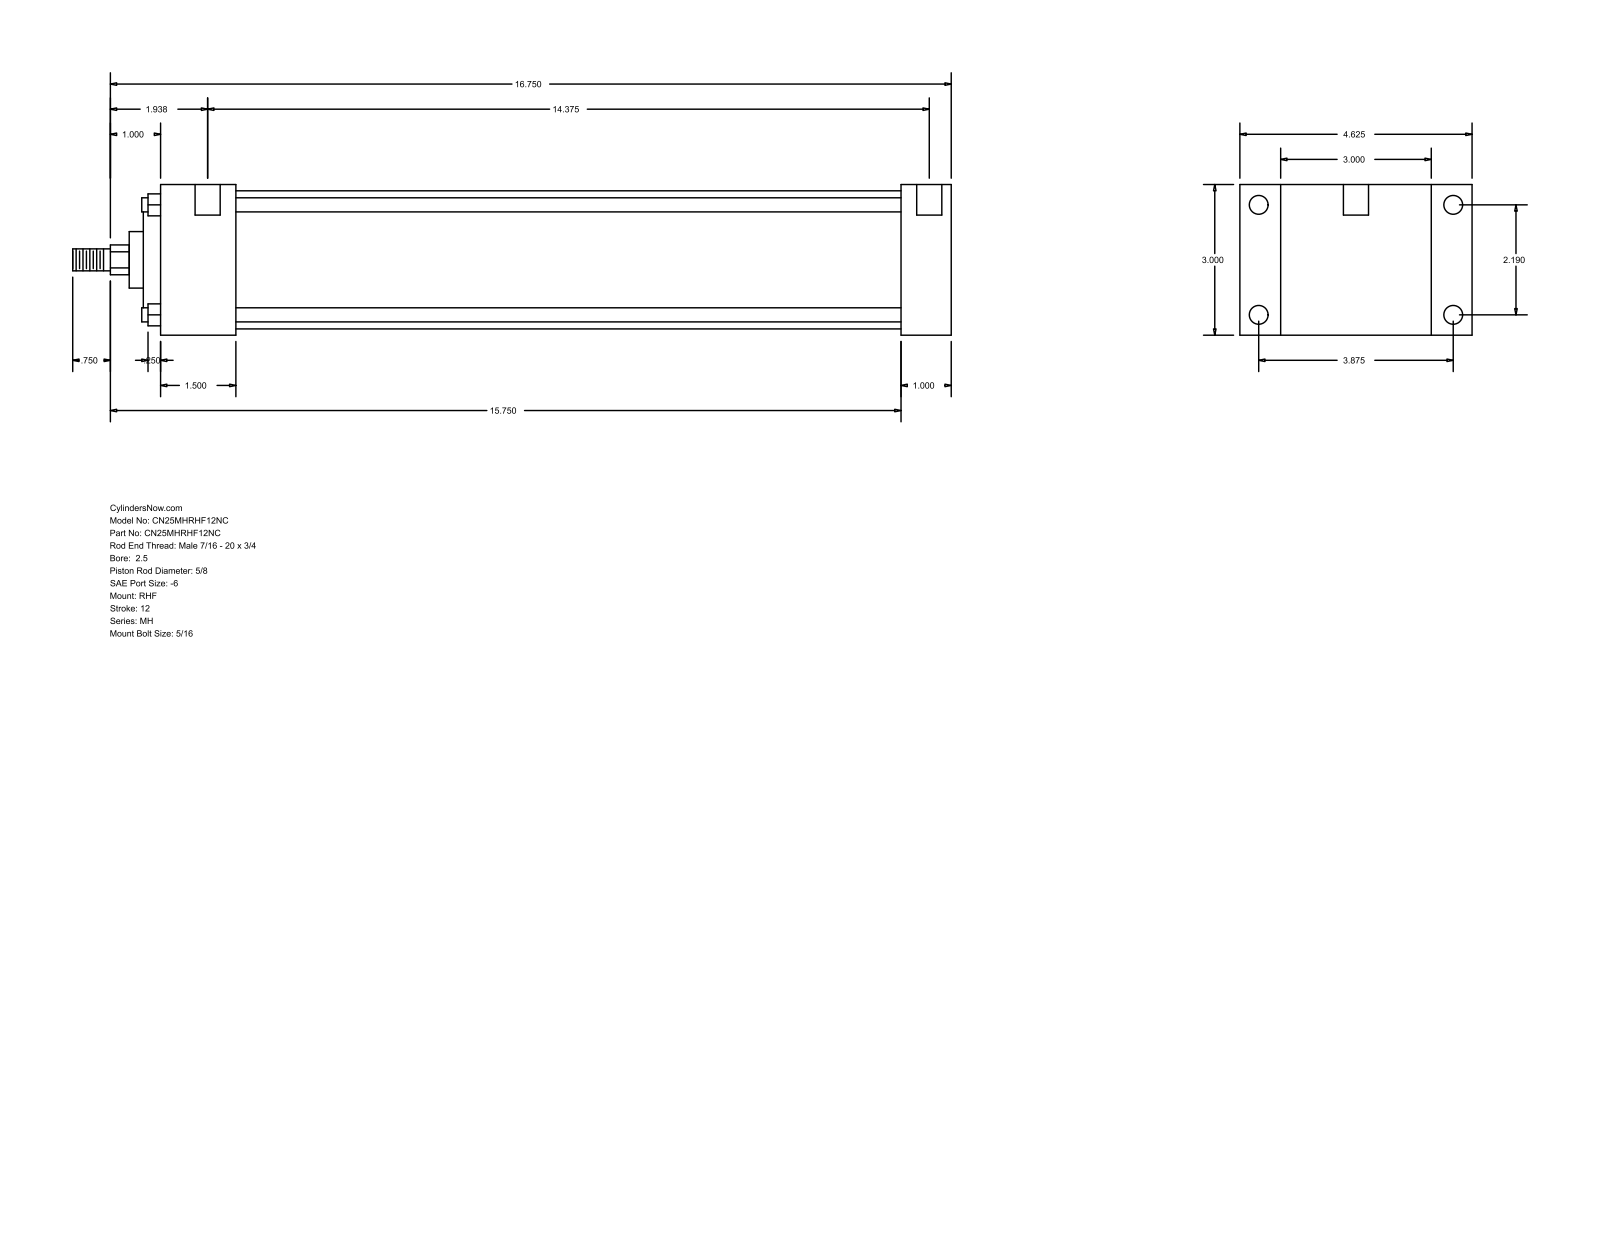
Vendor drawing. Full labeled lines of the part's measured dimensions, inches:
Part name (STEP PRODUCT): MH_RHF__0250_0.625
STEP written by: GSSL Pune (CONFIG_CONTROL_DESIGN)
Units: inches
Bodies: 0 solids, 90 faces (61 planar, 29 cylindrical, 0 other)
Overall size (bounding box): 17.5 × 4.625 × 3
Round holes (diameter × count): ⌀0.219 ×4, ⌀0.375 ×4, ⌀0.5 ×2
Round bosses / shafts (diameter × count): ⌀0.281 ×4, ⌀2.75 ×1, ⌀2.187 ×1, ⌀1.125 ×1, ⌀0.625 ×1, ⌀0.437 ×1
Partial cylindrical surfaces — rounded edges, fillets, slot ends (radius × count): R0.297 ×1
Main face-to-face distances: 3, 1, 0.813, 3.813, 15.75, 14.75, 1.5, 4.625, 13.25, 14.25
Hole centre spacings: 2.19, 3.875, 4.451, 14.687, 0.125, 0.187, 14.375, 14.5
